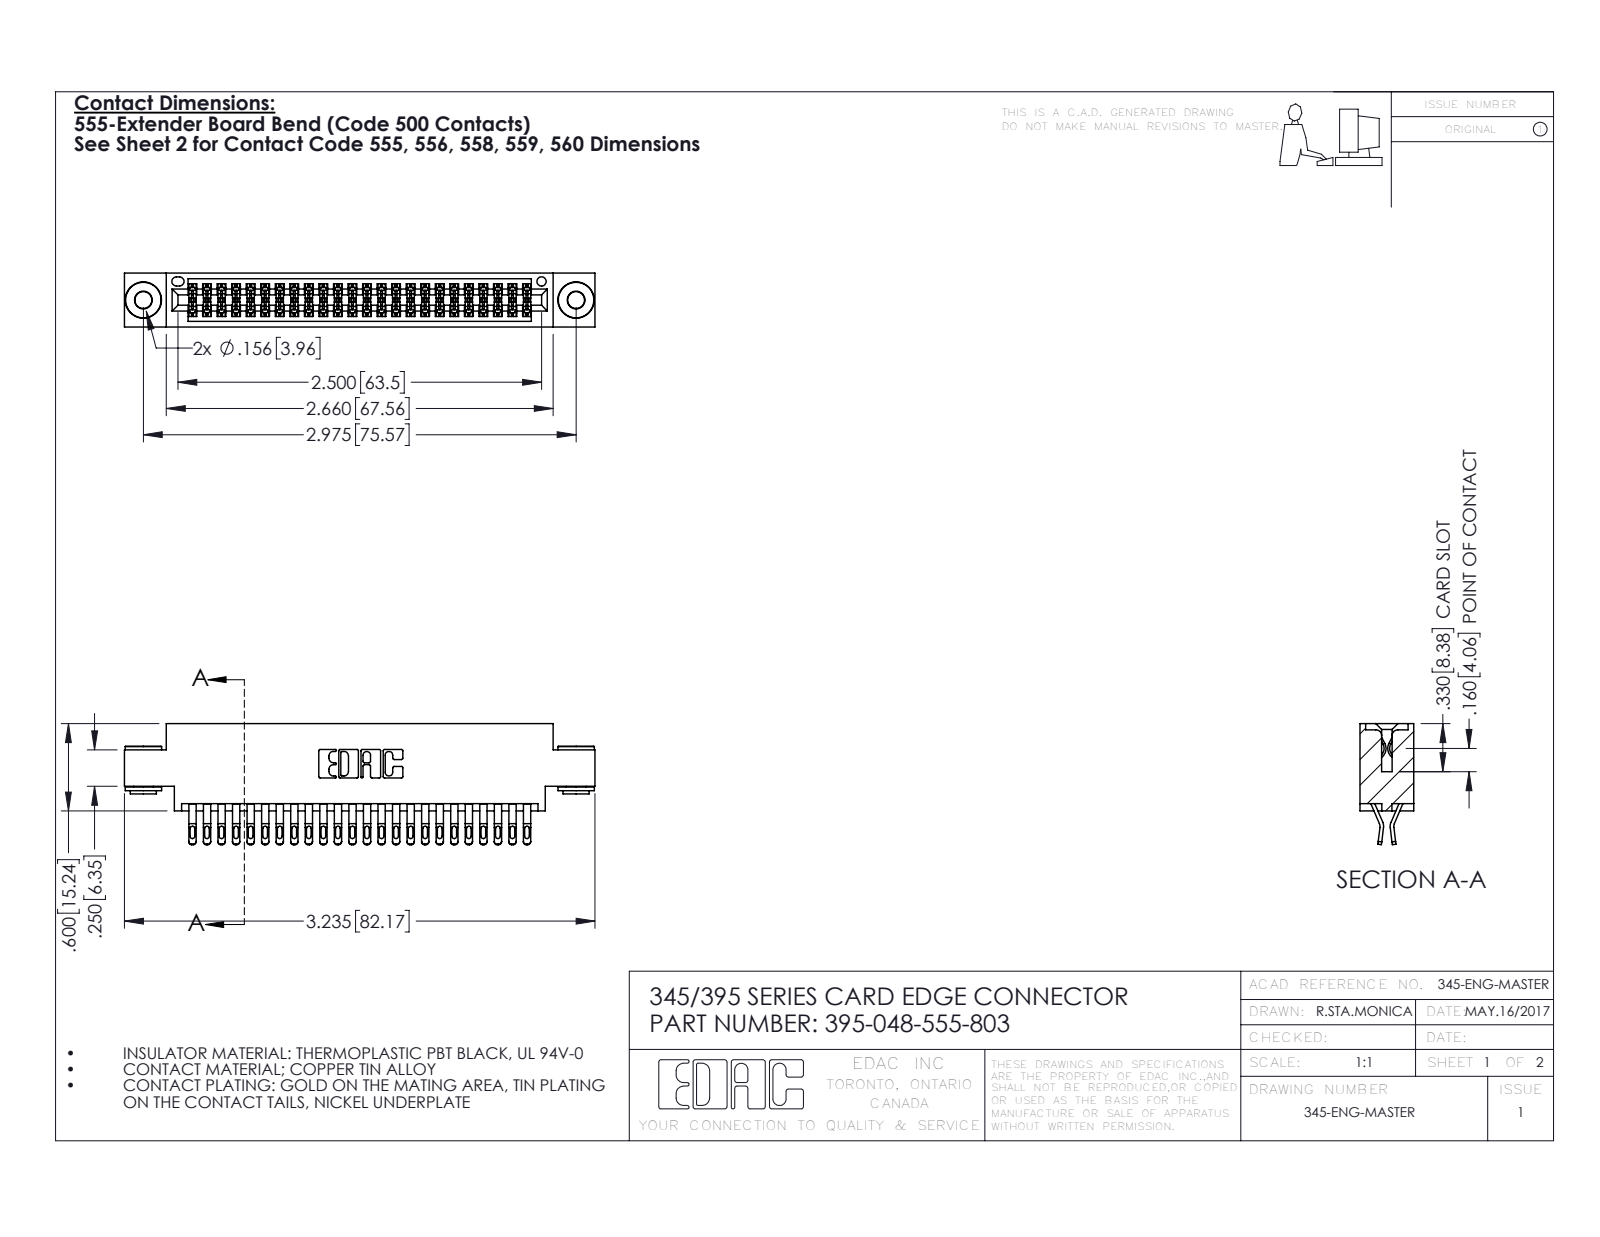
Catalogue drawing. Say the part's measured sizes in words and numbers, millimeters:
The part is named "395-048-555-803; 345 Part_0.170 Offset - 0.156 Dia-TH; 345-292-001_555 Tail; 345-250-002_345-250-002-102". Its 3-D file was written by "SolidWorks 2016 (CONFIG_CONTROL_DESIGN)". It is 51 solids with 2856 faces: 1582 planar, 1266 cylindrical and 8 other. Overall it measures 82.2 by 21.1 by 9.4 millimeters. Its volume is 7 870 cubic millimeters and its surface area 12 100 square millimeters. Round holes: 2 of diameter 2.9, 2 of diameter 4, 1 of diameter 1.6. Round bosses or shafts: 2 of diameter 6.4, 2 of diameter 4.6, 2 of diameter 3.5. Partial cylindrical surfaces (rounded edges, fillets, slot ends): 120 of radius 0.4, 96 of radius 0.5, 72 of radius 0.2, 22 of radius 0.3, 6 of radius 0.2, 6 of radius 0.8, 3 of radius 0.7, 2 of radius 0.3. The main face-to-face distances are 1.8, 7.6, 9.4, 5.1, 0.6, 2.5, 6.9, 5.7, 4.4, 3.8. The hole center spacings are 6.9, 69.6, 75.6.
